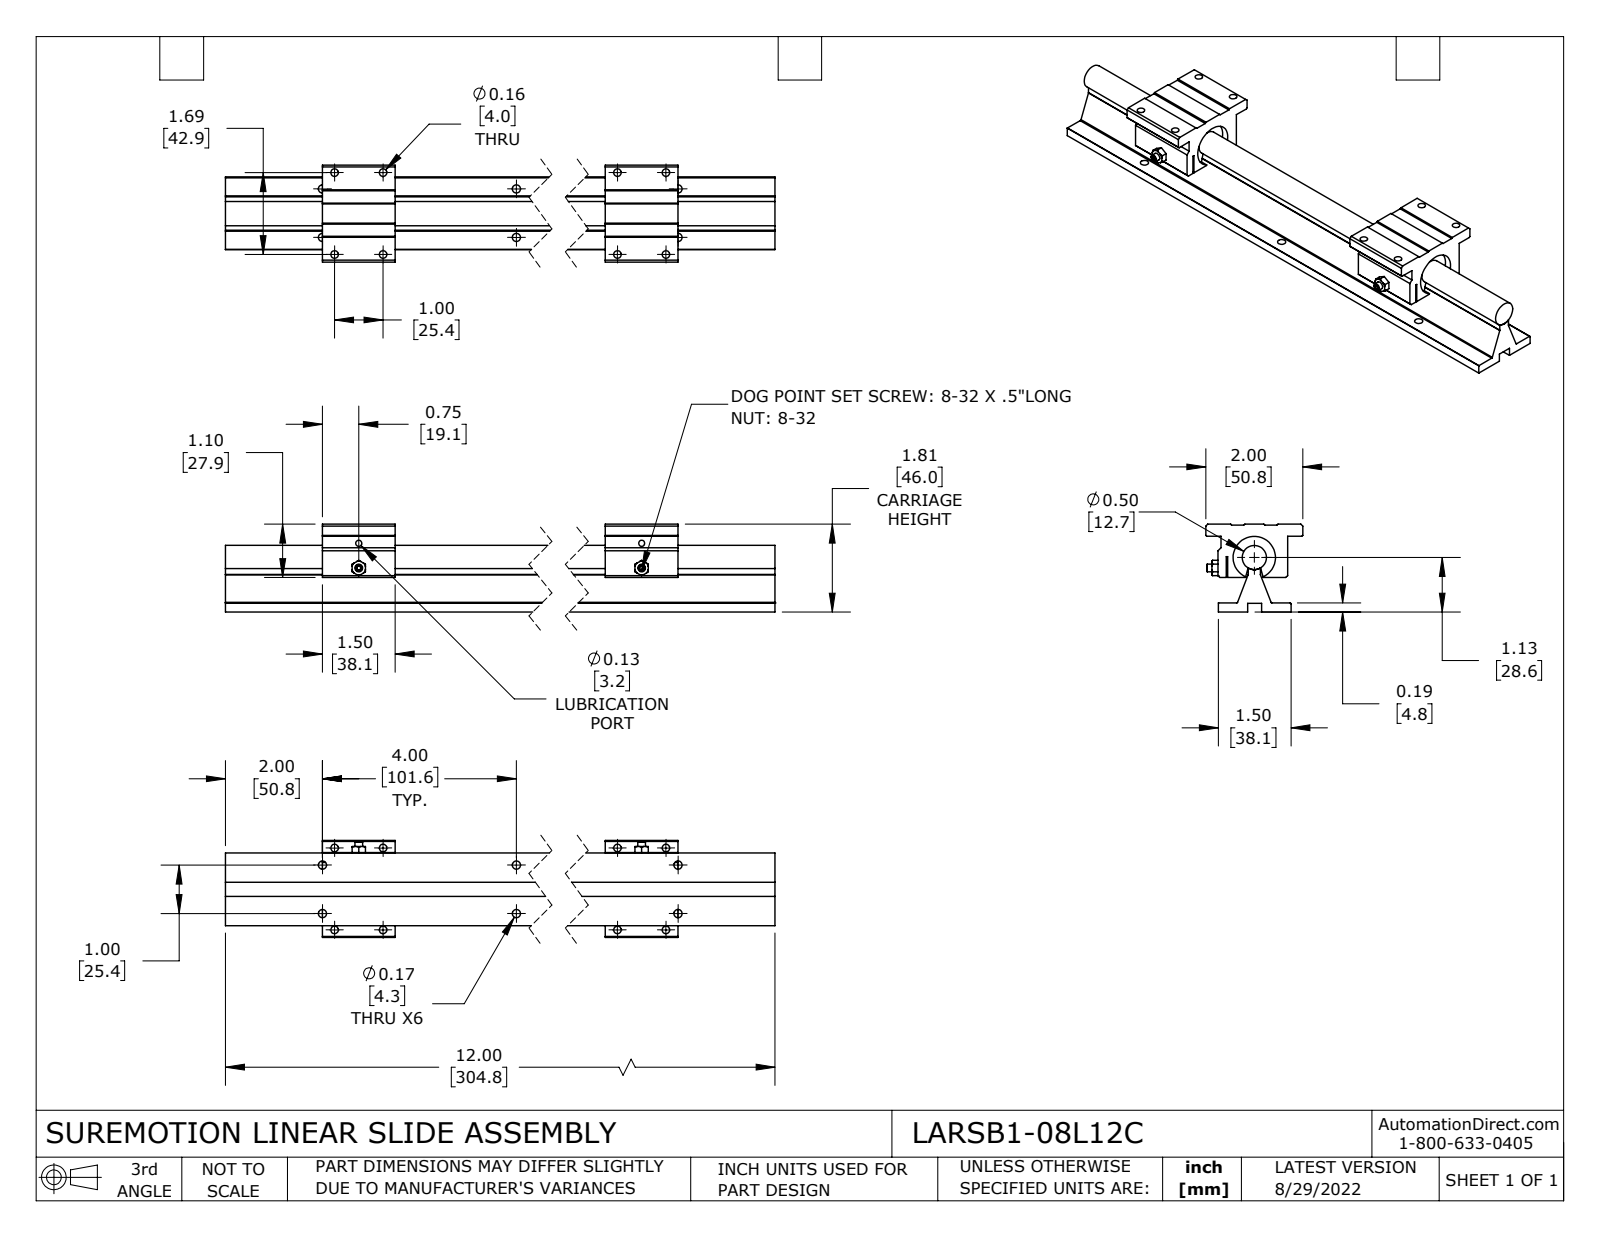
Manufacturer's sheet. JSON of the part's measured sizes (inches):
{"part_name": "LARSB1-08L12C; LARSB1-08L12C-RAIL; LARSACC-004", "step_written_by": "SolidWorks 2021 (CONFIG_CONTROL_DESIGN)", "units": "inches", "bodies": {"solids": 4, "faces": 204, "planar": 119, "cylindrical": 69, "other": 16}, "overall_size": [12, 2, 1.812], "volume_in3": 12.79, "surface_area_in2": 111, "round_holes": [[0.156, 8], [0.169, 6], [0.126, 2], [0.5, 1], [0.874, 1]], "round_bosses_or_shafts": [[0.157, 2]], "partial_cylinders_radius": [[0.02, 8], [0.04, 1], [0.249, 1]], "face_to_face_distances": [0.187, 1.5, 0.605, 0.895, 1.812, 1.625, 0.25, 0.18, 1.632, 0.525], "hole_center_spacings": [1, 6.5, 1.688, 1.962, 4, 4.123, 6.716, 0.419]}
